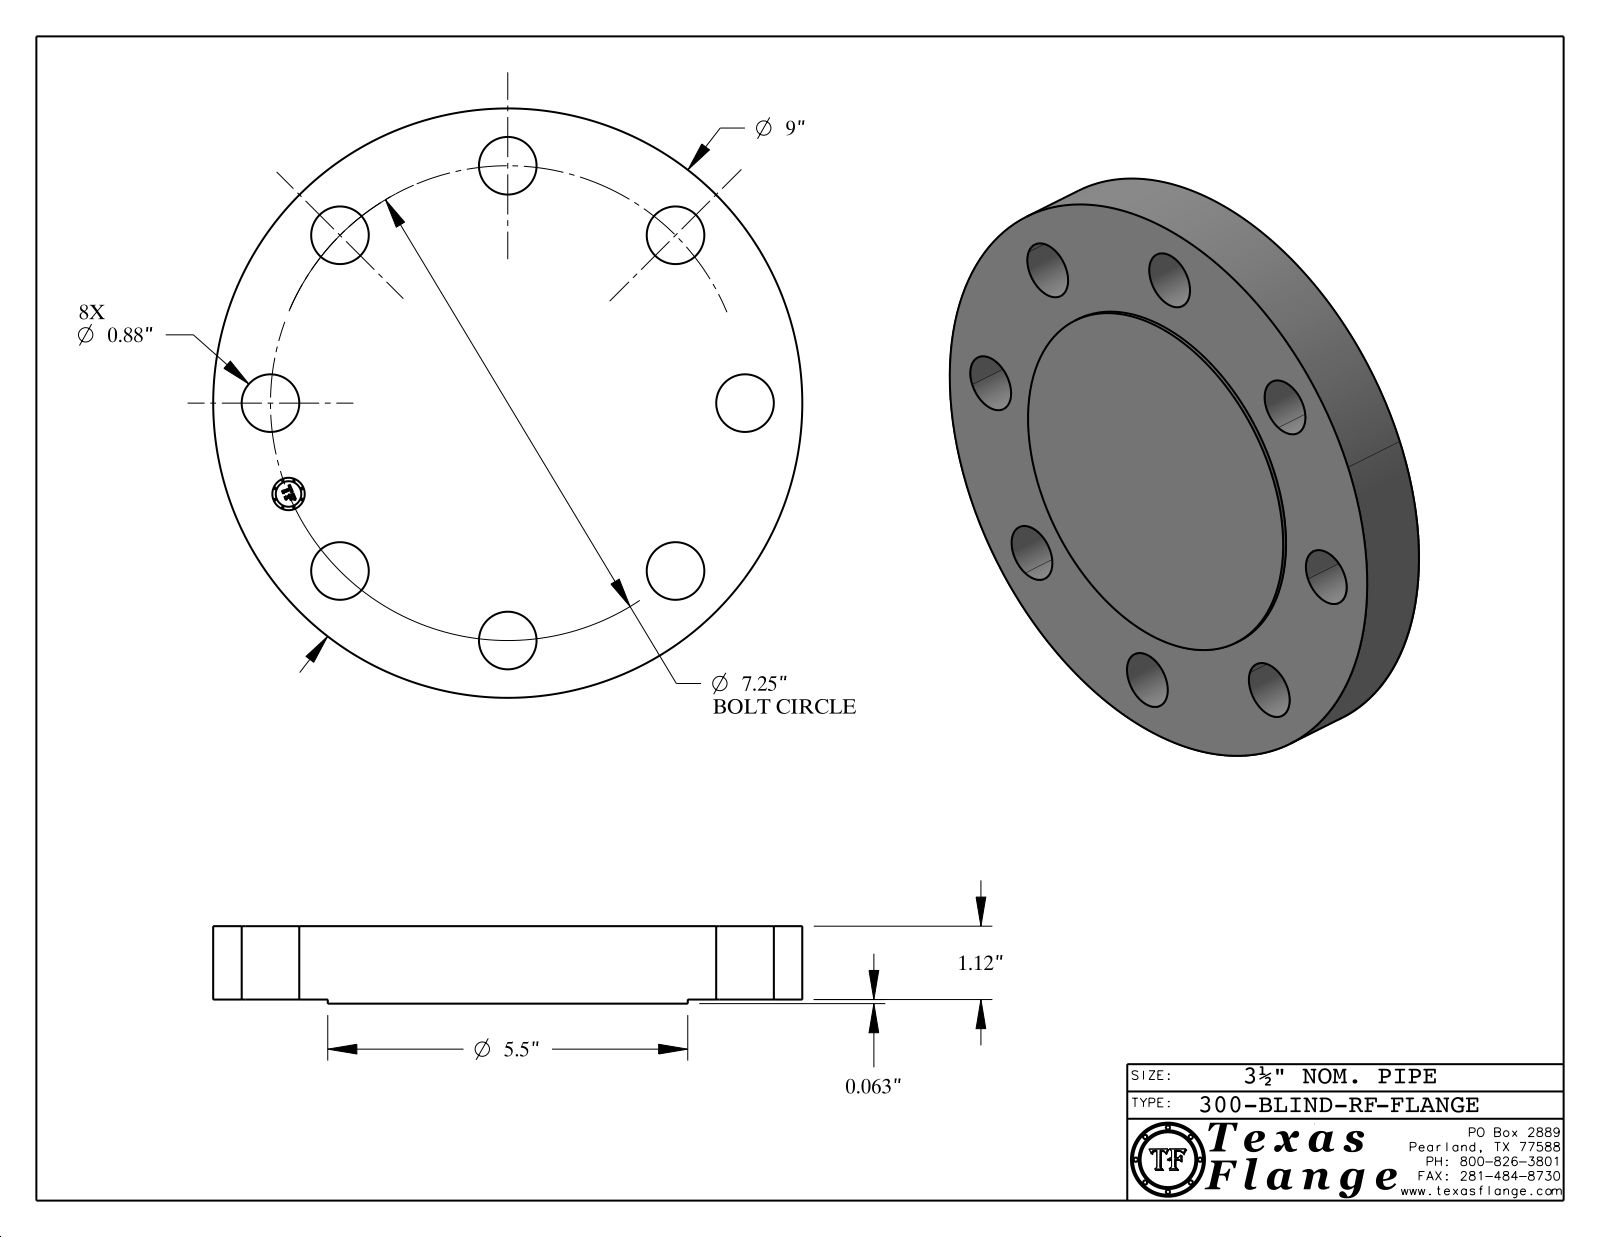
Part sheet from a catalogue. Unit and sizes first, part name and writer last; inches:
Units: inches
Overall size (bounding box): 9 × 9 × 1.183
Round holes (diameter × count): ⌀0.88 ×8, ⌀0.495 ×1
Round bosses / shafts (diameter × count): ⌀0.03 ×8, ⌀9 ×1, ⌀5.5 ×1, ⌀0.39 ×1
Main face-to-face distances: 1.12, 0.063, 1.183, 1.168, 1.105, 0.015, 0.148, 0.144, 0.027, 0.096
Hole centre spacings: 2.774, 5.127, 6.698, 7.25, 1.415, 7.111, 4.028, 4.028
Volume: 67.29 in³ · Surface area: 175.1 in²
Bodies: 1 solid, 408 faces (368 planar, 40 cylindrical, 0 other)
Part name (STEP PRODUCT): 300-BLIND-RF
STEP written by: CATIA V5 STEP AP214 (AUTOMOTIVE_DESIGN)
